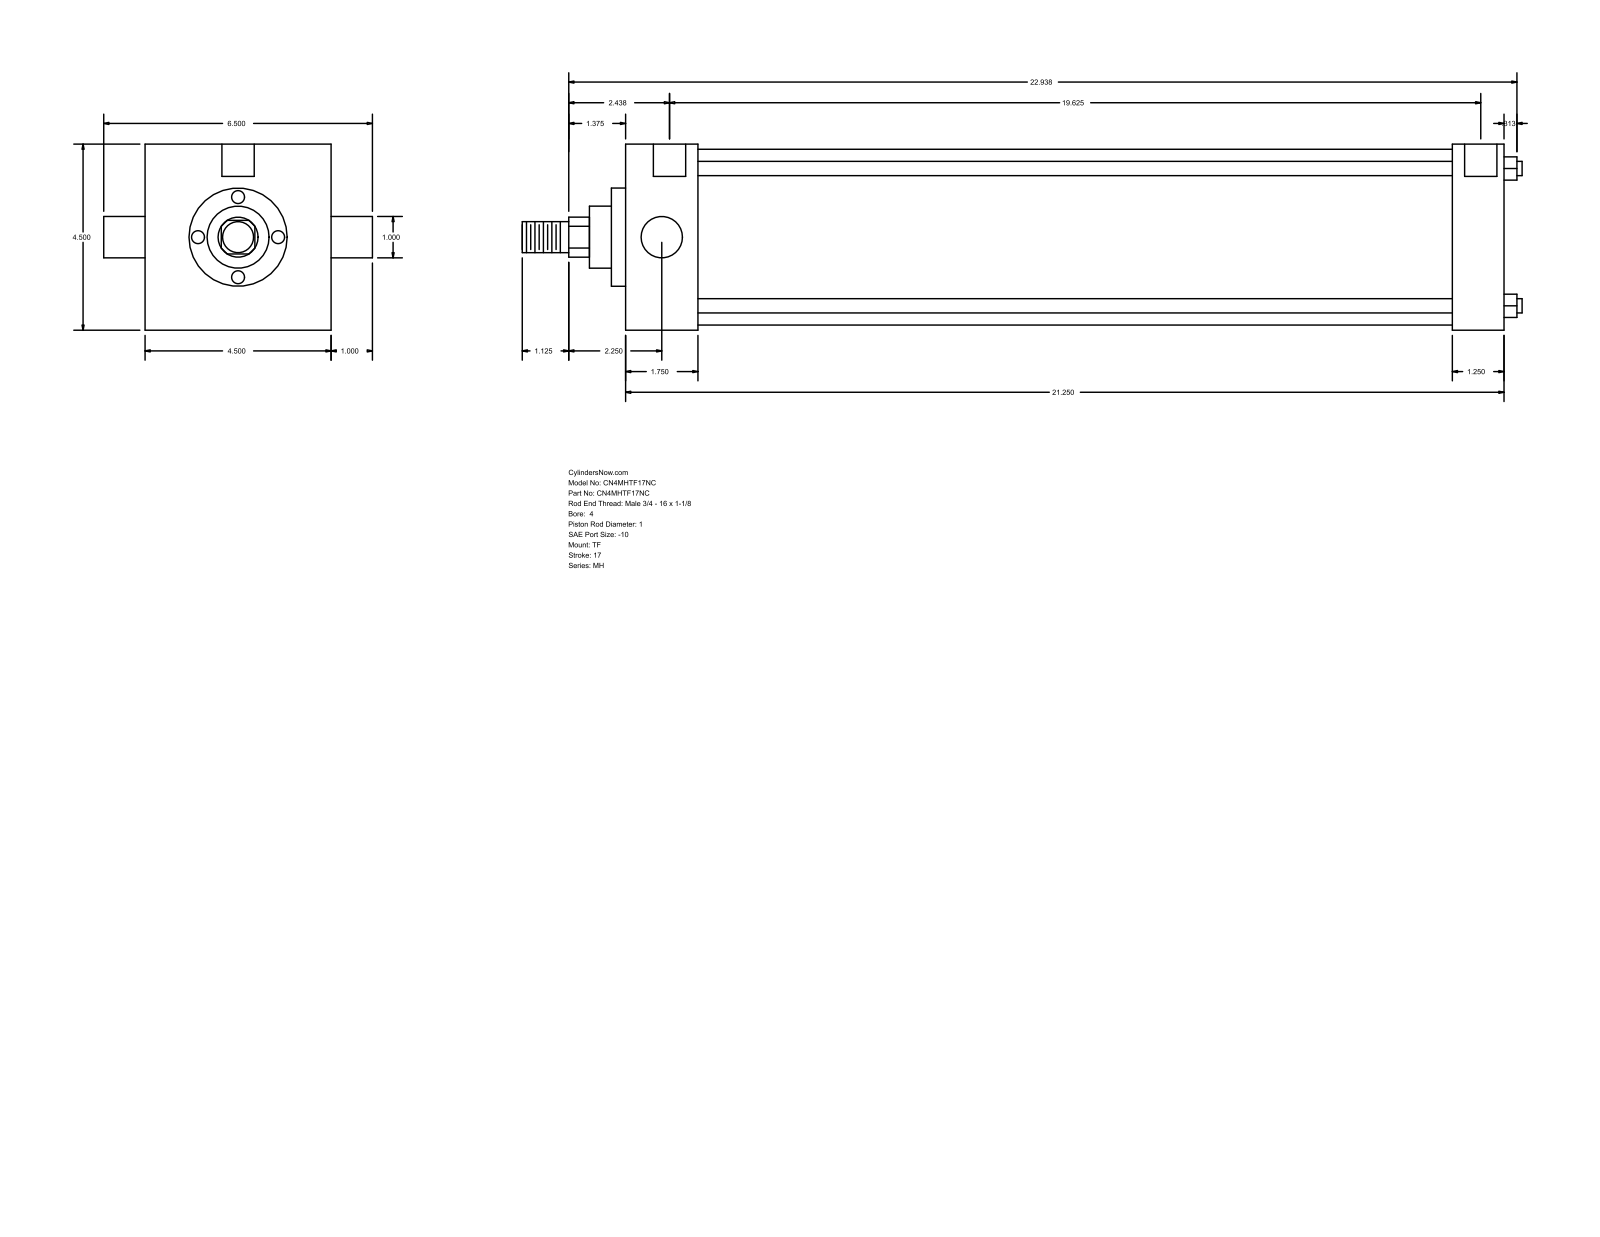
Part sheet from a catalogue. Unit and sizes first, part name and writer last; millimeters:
Units: millimetres
Overall size (bounding box): 614.36 × 165.1 × 114.3
Round holes (diameter × count): ⌀8.73 ×3, ⌀19.84 ×2
Round bosses / shafts (diameter × count): ⌀8.76 ×4, ⌀25.4 ×2, ⌀107.95 ×1, ⌀60.33 ×1, ⌀38.1 ×1, ⌀19.05 ×1
Partial cylindrical surfaces — rounded edges, fillets, slot ends (radius × count): R12.29 ×1
Main face-to-face distances: 114.3, 539.75, 44.46, 495.29, 508, 463.54, 31.75, 8.73, 53.19, 516.73
Hole centre spacings: 1.58, 1.59, 498.48, 500.06, 500.07, 501.65
Bodies: 0 solids, 86 faces (61 planar, 25 cylindrical, 0 other)
Part name (STEP PRODUCT): MH_TF__0400_1
STEP written by: GSSL Pune (CONFIG_CONTROL_DESIGN)
